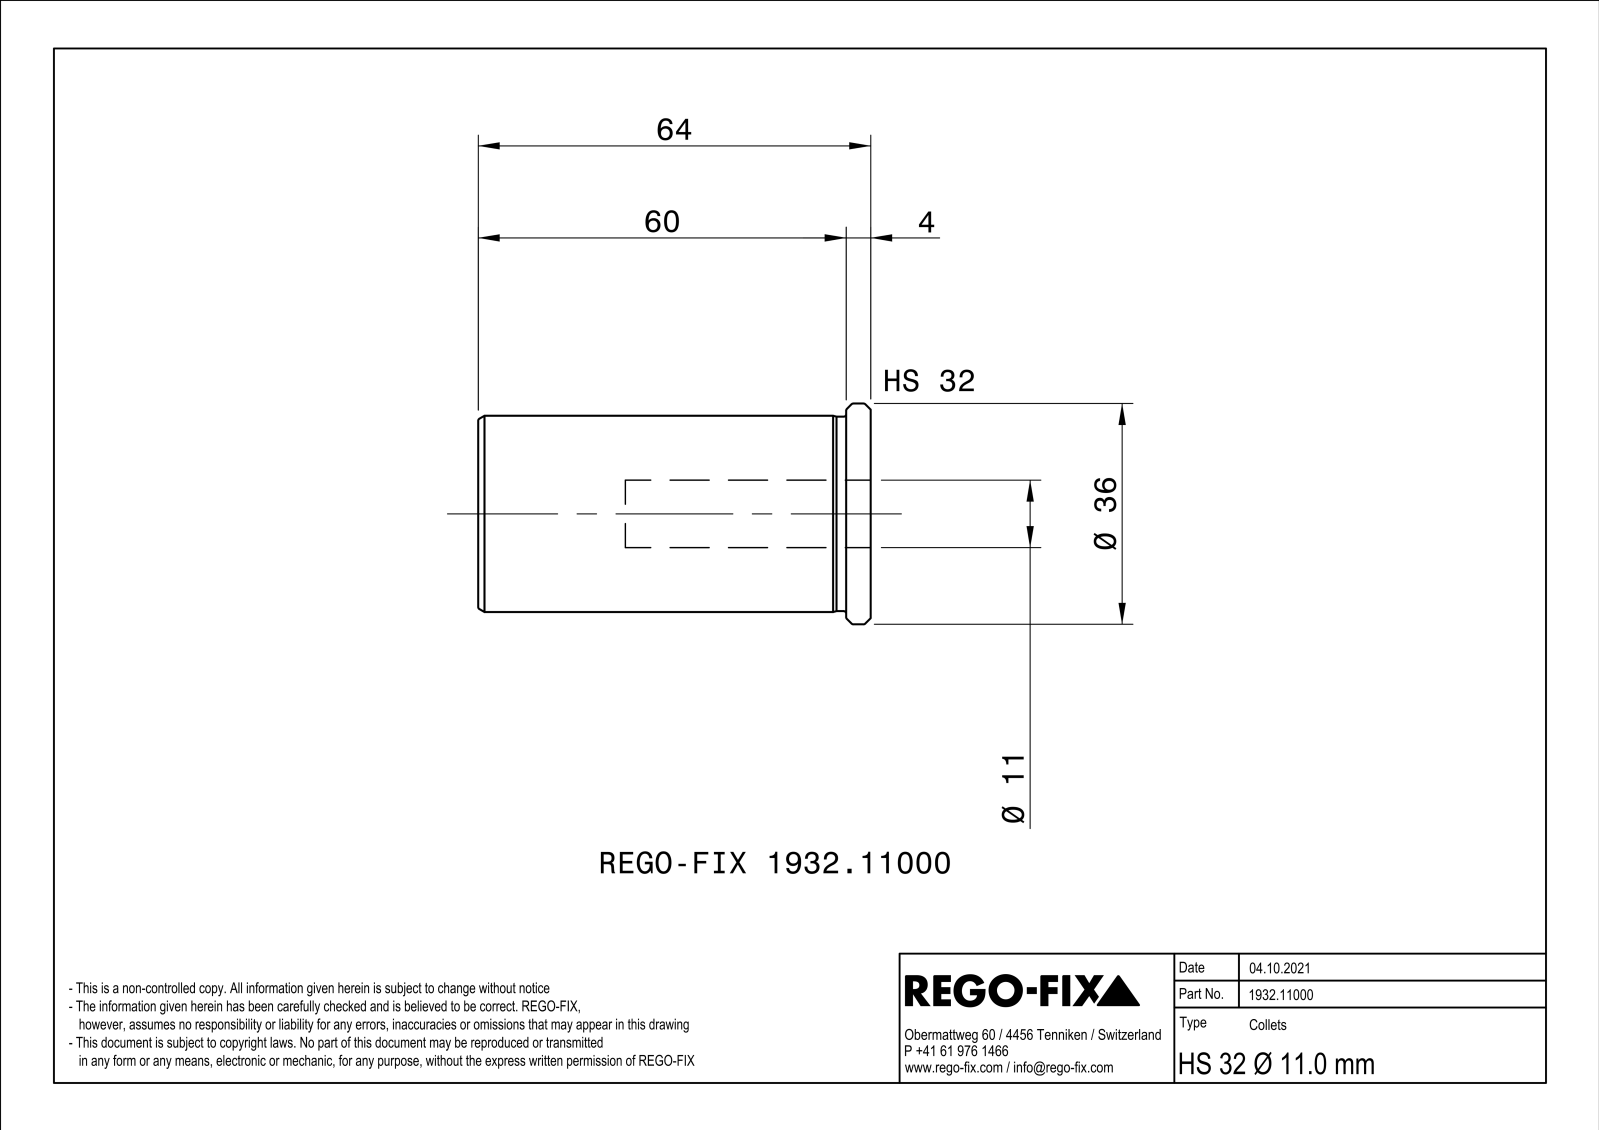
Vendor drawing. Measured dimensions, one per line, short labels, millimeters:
name: NOCUT
written by: SIEMENS PLM Software Solid Edge ST10 (AUTOMOTIVE_DESIGN)
unit: mm
bodies: 1 solid, 71 faces (22 planar, 11 cylindrical, 38 other)
size: 64 × 35.99 × 35.99
volume: 35 997 mm³; area: 14 147 mm²
holes: 1× ⌀11, 1× ⌀26.5
bosses: 1× ⌀36, 1× ⌀32, 1× ⌀31.7
face distances: 1, 64, 4, 60
